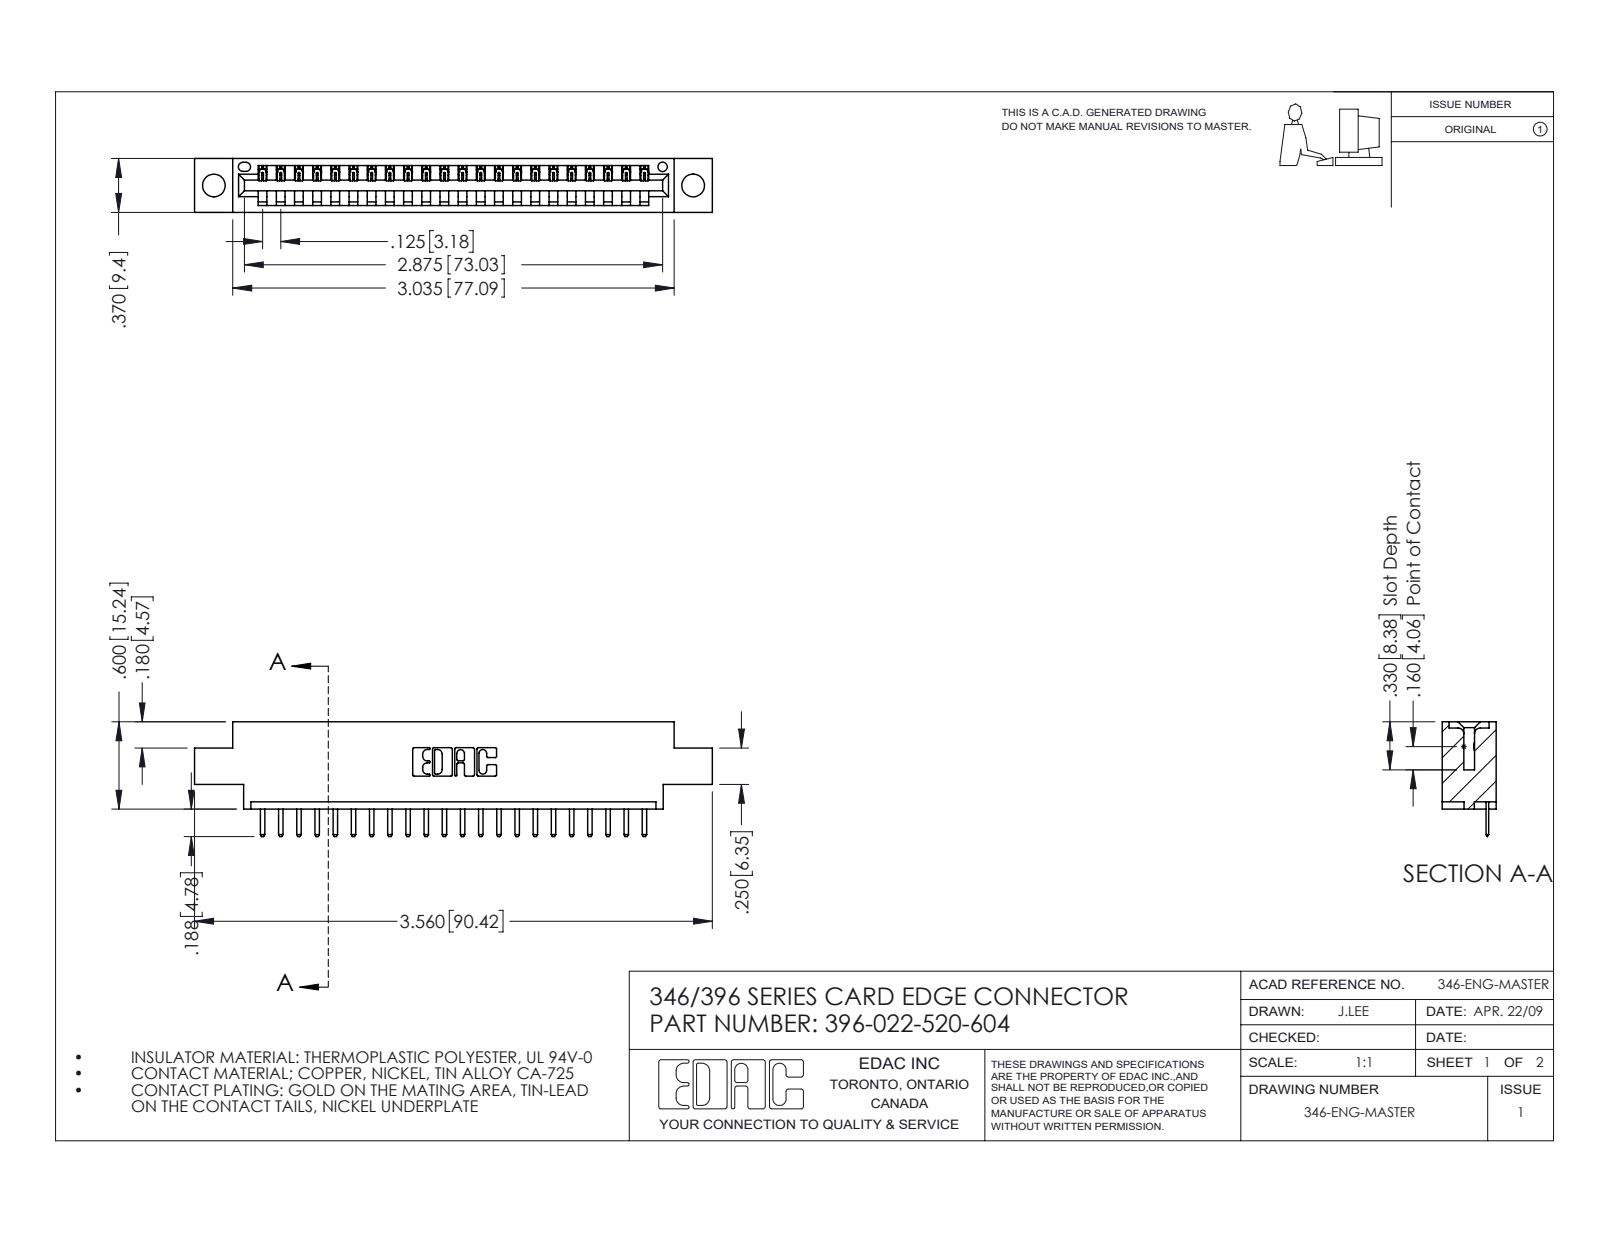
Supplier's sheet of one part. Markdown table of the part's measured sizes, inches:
| quantity | value |
| --- | --- |
| part name | 345-292-001_345-293-120; 396-022-520-604; 346 Part_0.170 Offset - 0.156 Dia-TH |
| STEP written by | SolidWorks 2016 (CONFIG_CONTROL_DESIGN) |
| units | inches |
| bodies | 23 solids, 1490 faces (1004 planar, 486 cylindrical, 0 other) |
| overall size | 3.56 × 0.788 × 0.37 |
| volume | 0.501 in³ |
| surface area | 15.19 in² |
| round holes (diameter × count) | 0.156 × 2, 0.064 × 1 |
| partial cylindrical surfaces (radius × count) | 0.01 × 46, 0.006 × 44, 0.01 × 22, 0.007 × 6, 0.031 × 6, 0.026 × 3, 0.031 × 2, 0.04 × 2 |
| main face-to-face distances | 0.37, 0.048, 0.322, 0.25, 0.148, 0.222, 0.1, 0.174, 0.072, 0.298 |
| hole center spacings | 0.246, 3.087, 3.295 |
